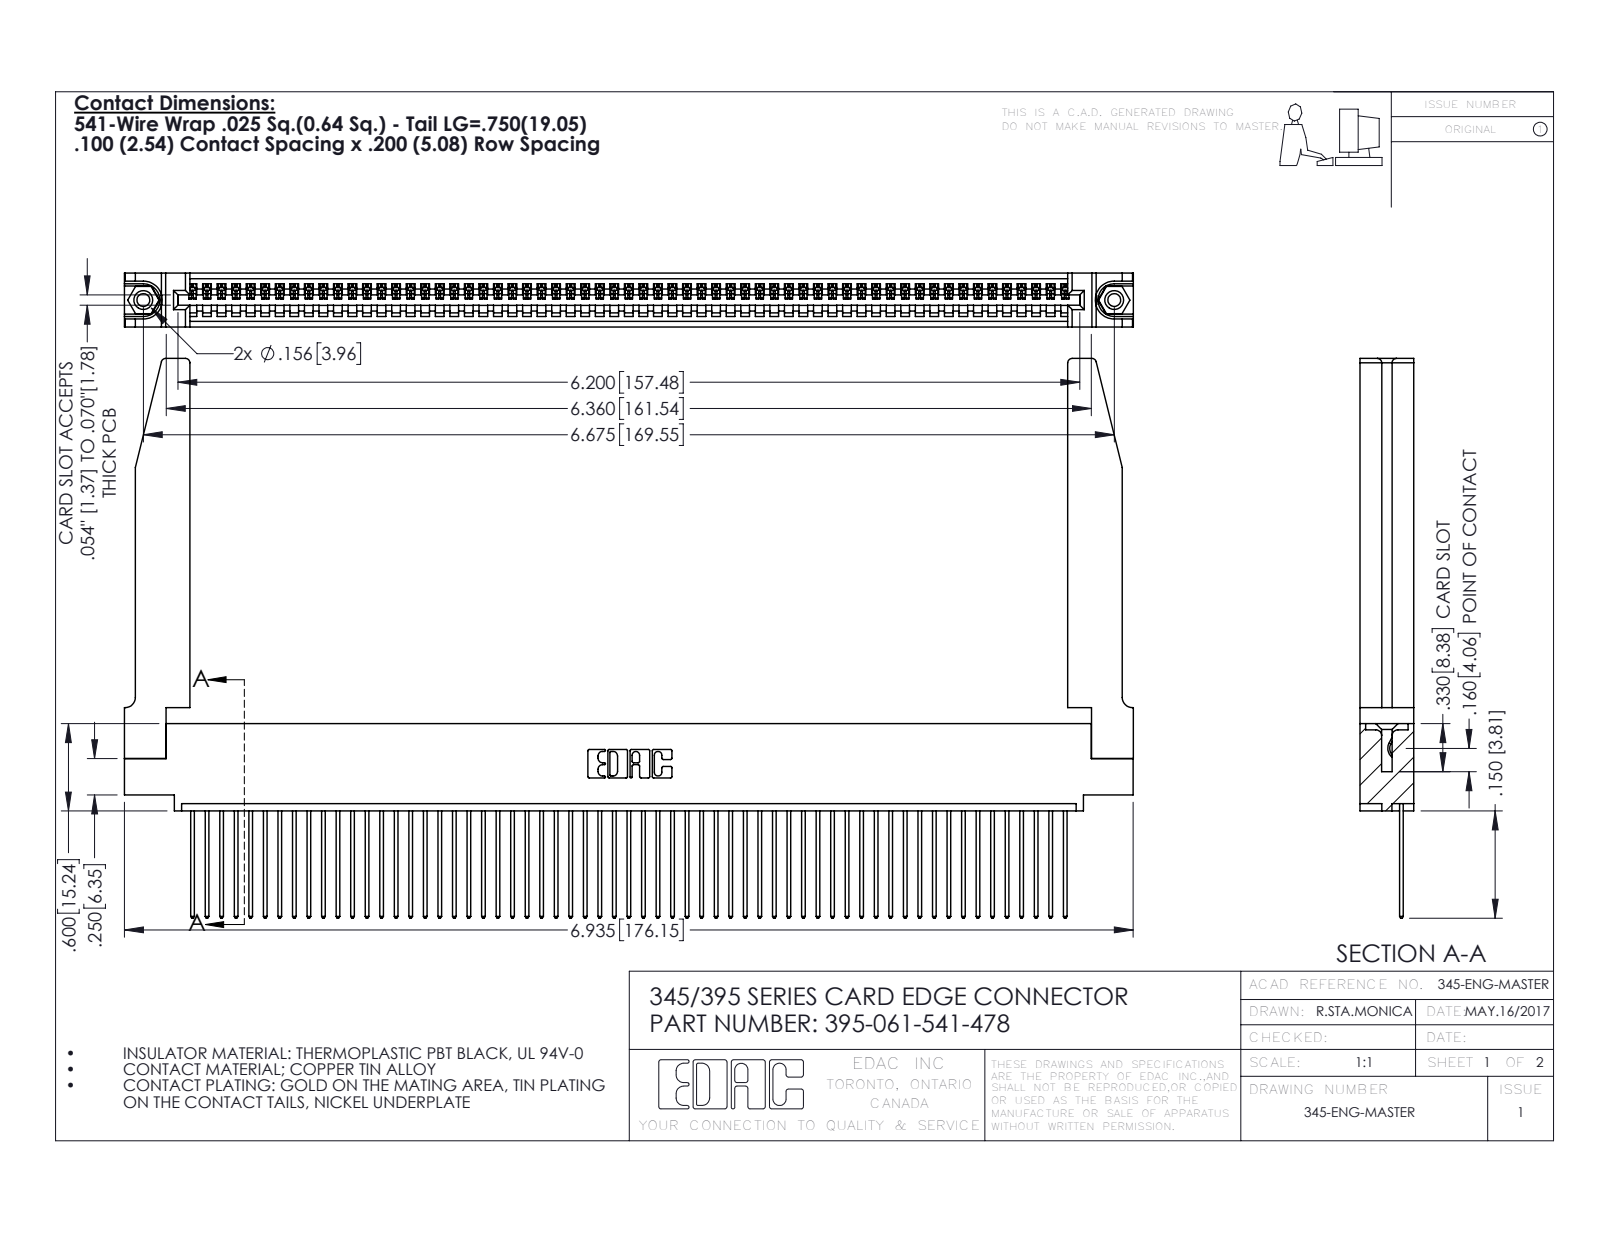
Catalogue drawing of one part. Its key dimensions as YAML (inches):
part_name: "395-061-541-478; 345-250-001_345-250-001-102; 345-292-001_345-293-141; 345-220-078_345-220-078 (+1 more)"
step_written_by: "SolidWorks 2016 (CONFIG_CONTROL_DESIGN)"
units: inches
bodies: {solids: 66, faces: 3902, planar: 2666, cylindrical: 1184, other: 52}
overall_size: [6.936, 3.847, 0.37]
volume: 1.513
surface_area: 48.03
round_holes:
  - {diameter: 0.089, count: 2}
  - {diameter: 0.125, count: 2}
  - {diameter: 0.156, count: 2}
  - {diameter: 0.064, count: 1}
round_bosses_or_shafts:
  - {diameter: 0.155, count: 2}
partial_cylinders:
  - {radius: 0.006, count: 122}
  - {radius: 0.01, count: 122}
  - {radius: 0.01, count: 22}
  - {radius: 0.03, count: 8}
  - {radius: 0.007, count: 6}
  - {radius: 0.031, count: 6}
  - {radius: 0.026, count: 3}
  - {radius: 0.031, count: 2}
face_to_face_distances: [0.072, 0.298, 0.37, 0.098, 0.272, 0.025, 0.2, 0.225, 0.148, 0.15]
hole_center_spacings: [0.27, 6.439, 6.675]
